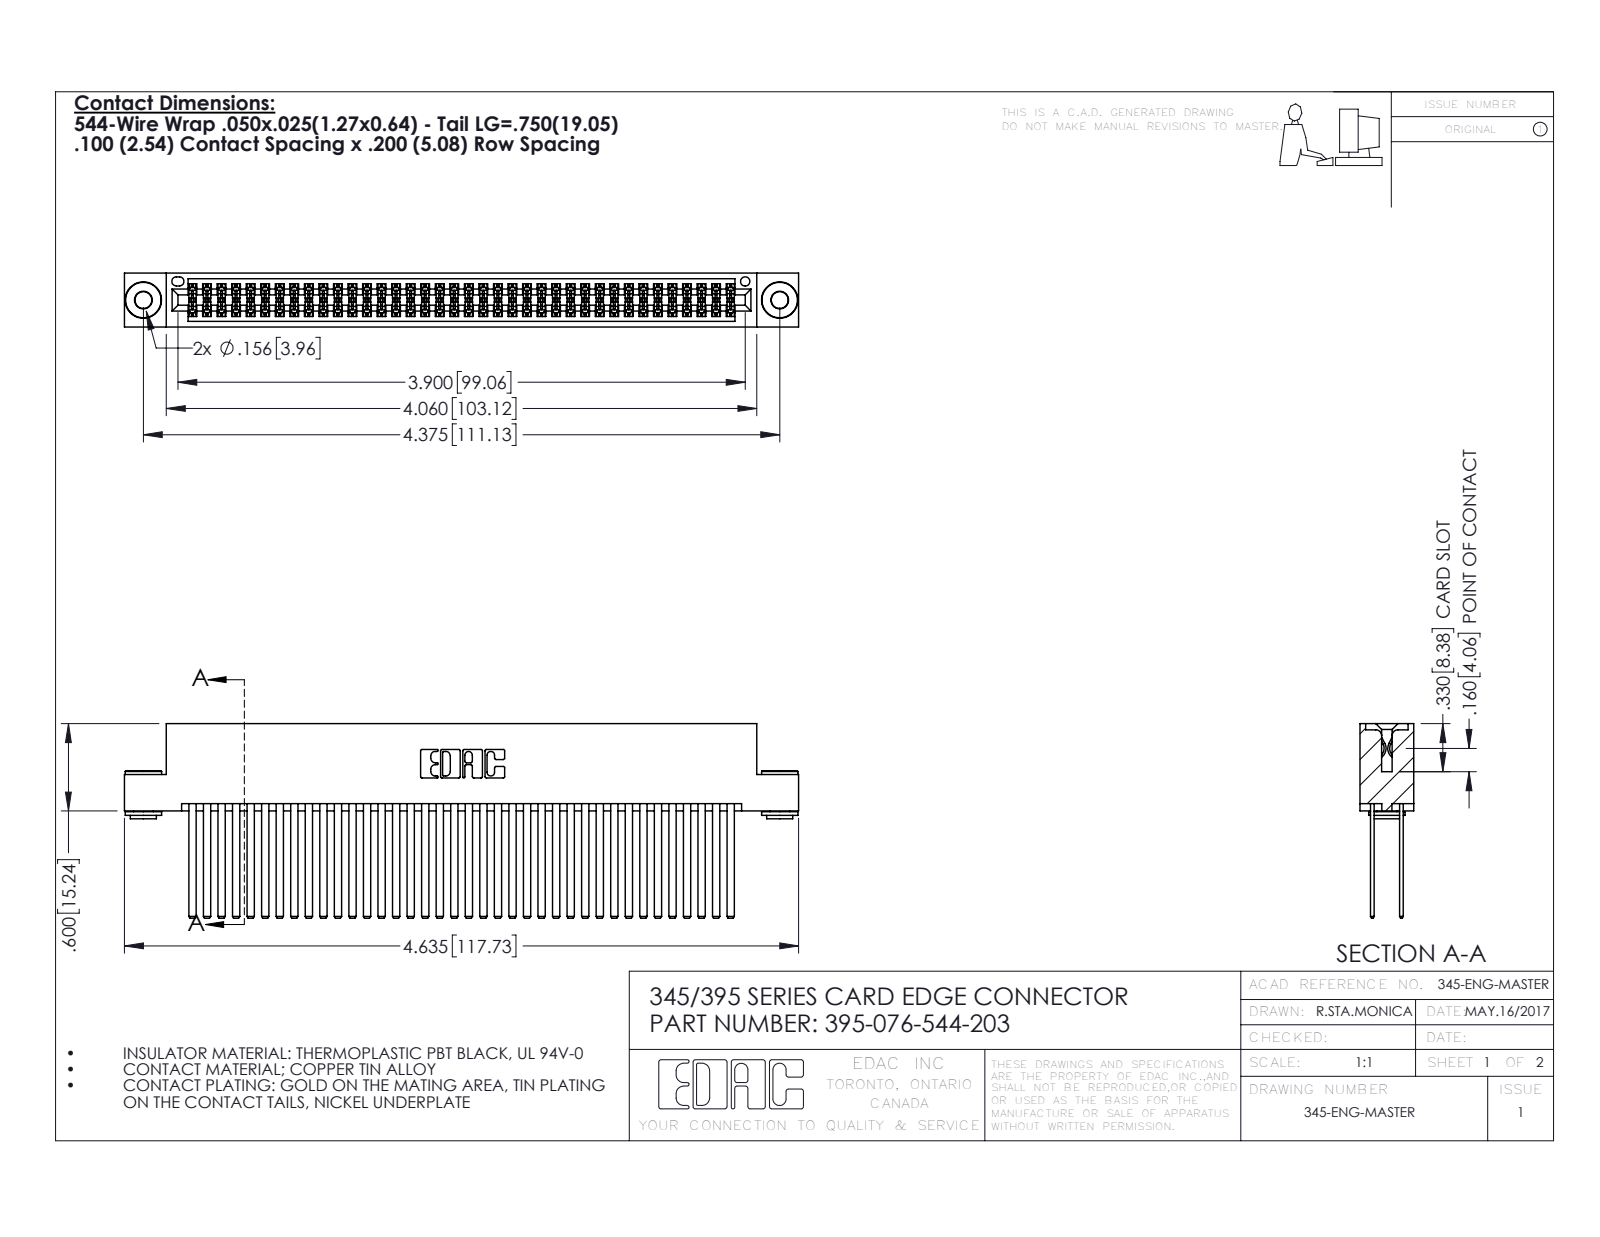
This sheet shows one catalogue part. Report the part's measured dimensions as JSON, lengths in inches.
{"part_name": "345 Part_Flush Mounting Lugs - 0.156 Dia-TH; 345-250-002_345-250-002-102; 345-292-001_345-293-144; 395-076-544-203", "step_written_by": "SolidWorks 2016 (CONFIG_CONTROL_DESIGN)", "units": "inches", "bodies": {"solids": 79, "faces": 3508, "planar": 2294, "cylindrical": 1206, "other": 8}, "overall_size": [4.635, 1.337, 0.37], "volume_in3": 0.762, "surface_area_in2": 33.64, "round_holes": [[0.116, 2], [0.156, 2], [0.064, 1]], "round_bosses_or_shafts": [[0.25, 2], [0.18, 2], [0.136, 2]], "partial_cylinders_radius": [[0.006, 114], [0.01, 22], [0.007, 6], [0.031, 6], [0.026, 3], [0.014, 2], [0.019, 2], [0.022, 2]], "face_to_face_distances": [0.2, 0.025, 0.072, 0.098, 0.272, 0.298, 0.225, 0.175, 0.37, 0.05], "hole_center_spacings": [0.27, 4.139, 4.375]}
